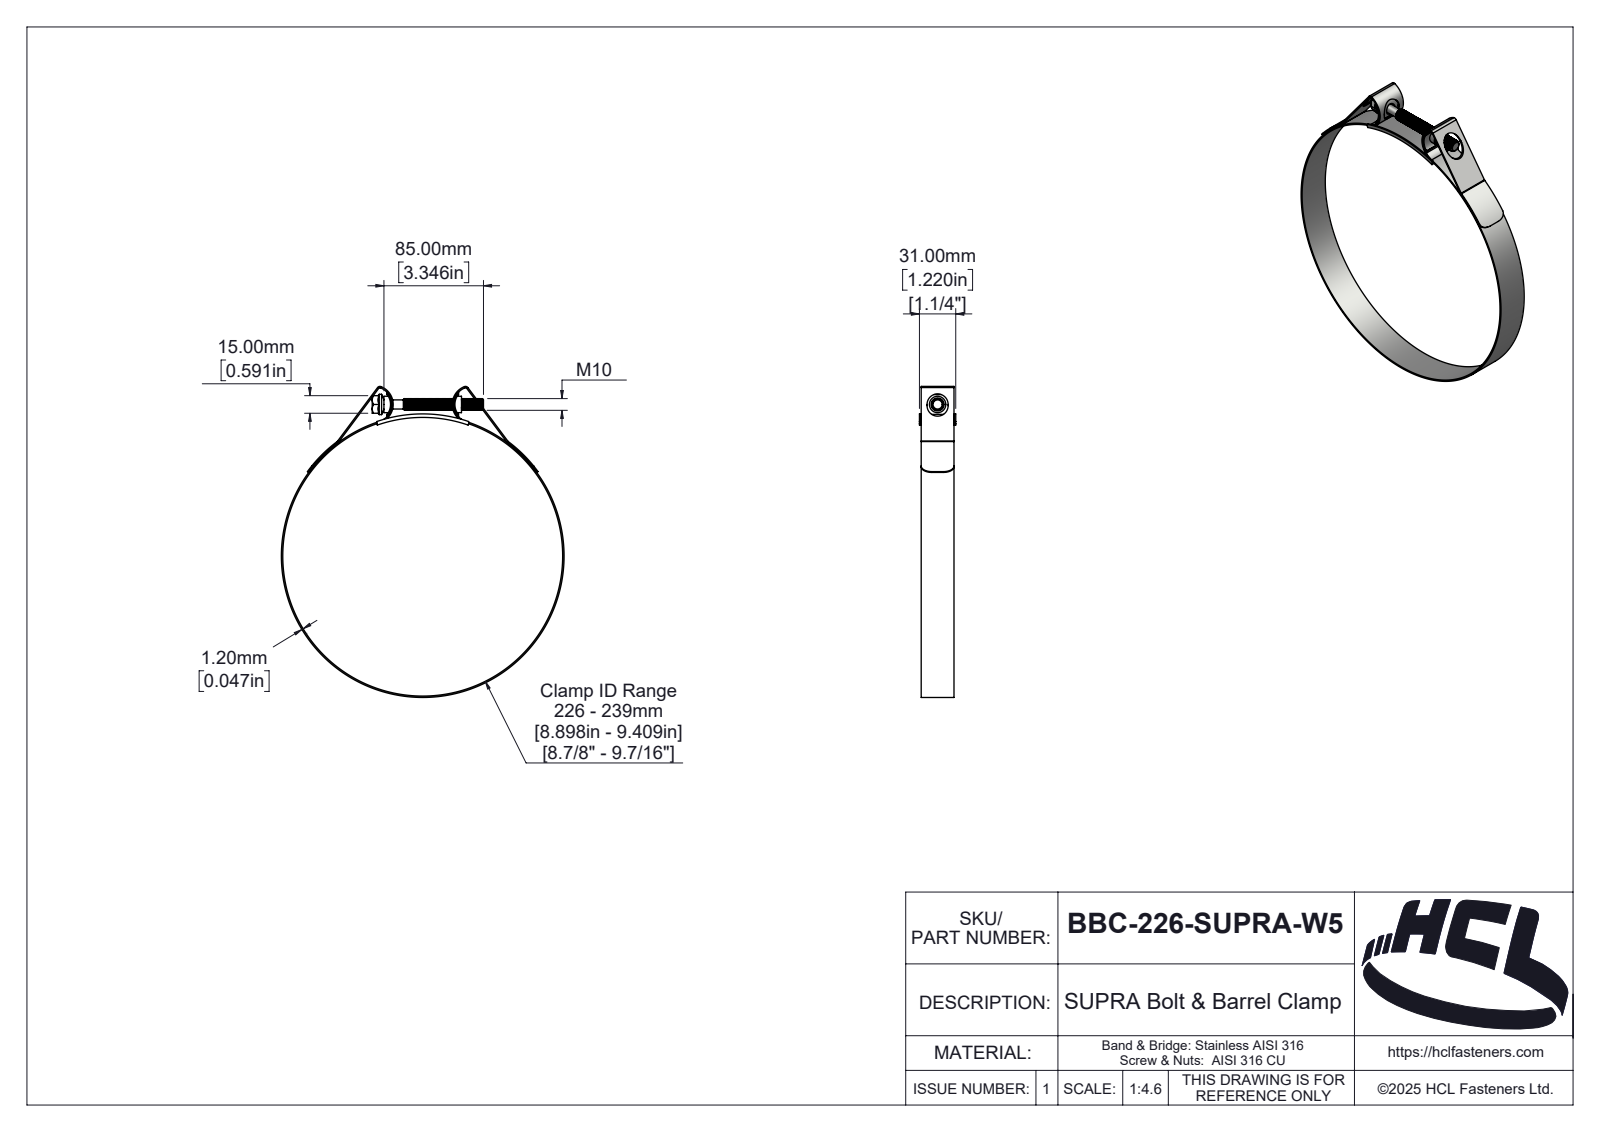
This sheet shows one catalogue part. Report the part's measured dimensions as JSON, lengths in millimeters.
{"part_name": "BBC-226-SUPRA-W5", "step_written_by": "SolidWorks 2025 (AUTOMOTIVE_DESIGN)", "units": "millimeters", "bodies": {"solids": 5, "faces": 381, "planar": 50, "cylindrical": 245, "other": 86}, "overall_size": [265.48, 241.4, 31], "volume_mm3": 42938, "surface_area_mm2": 66667, "round_holes": [[239, 1]], "round_bosses_or_shafts": [[241.4, 1], [17.32, 1], [14, 1], [10, 1], [7.8, 1]], "partial_cylinders_radius": [[1, 4], [1.3, 2], [2, 2], [2.5, 2], [3.2, 2], [9, 2], [14.06, 2], [15.06, 2]], "face_to_face_distances": [1.2, 28, 1.5, 29.5, 29.8, 28.3, 31, 28.6, 15, 2.5]}
